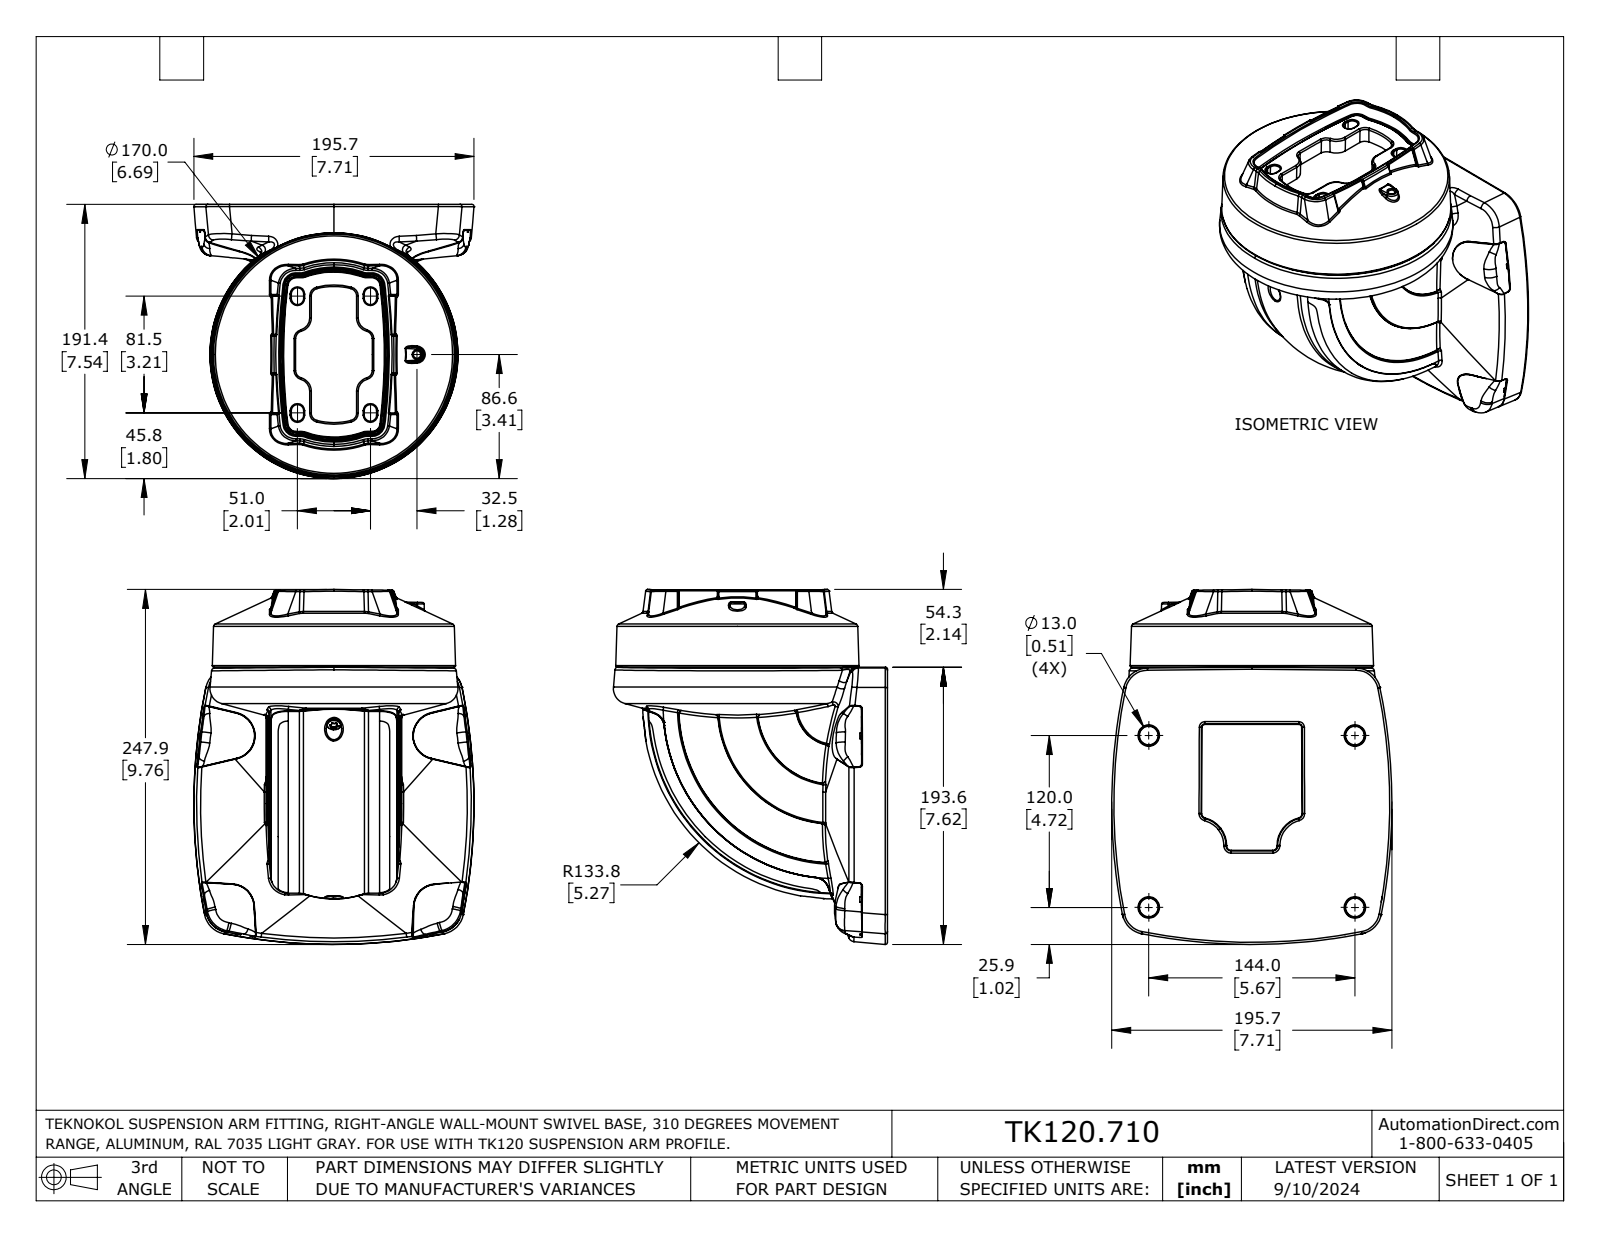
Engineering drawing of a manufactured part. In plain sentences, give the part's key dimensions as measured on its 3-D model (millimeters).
The part is named "TK120.710_REV4". Its 3-D file was written by "SolidWorks 2023 (AUTOMOTIVE_DESIGN)". It is 1 solid with 1348 faces: 165 planar, 131 cylindrical and 1052 other. Overall it measures 247.9 by 195.7 by 191.5 millimeters. Its volume is 2 706 000 cubic millimeters and its surface area 321 400 square millimeters. Round holes: 4 of diameter 4.5, 2 of diameter 5, 2 of diameter 8.3, 1 of diameter 5.2, 1 of diameter 8.3, 1 of diameter 8.3, 1 of diameter 8.3, 1 of diameter 8.4, 1 of diameter 63.9. Round bosses or shafts: 4 of diameter 5, 2 of diameter 10, 2 of diameter 6, 1 of diameter 168, 1 of diameter 13, 1 of diameter 12.7, 1 of diameter 12.3, 1 of diameter 12.3. Partial cylindrical surfaces (rounded edges, fillets, slot ends): 12 of radius 0.1, 12 of radius 2.7, 10 of radius 1.2, 8 of radius 0.8, 8 of radius 2, 6 of radius 1.1, 5 of radius 1.5, 4 of radius 1.4. The main face-to-face distances are 1.5, 24.5, 10.3, 14.2, 7, 8.5, 46.9, 39.9, 38.4, 72.7. The hole center spacings are 40, 56.6, 80, 26, 30.6, 30.6, 41, 70.5.
